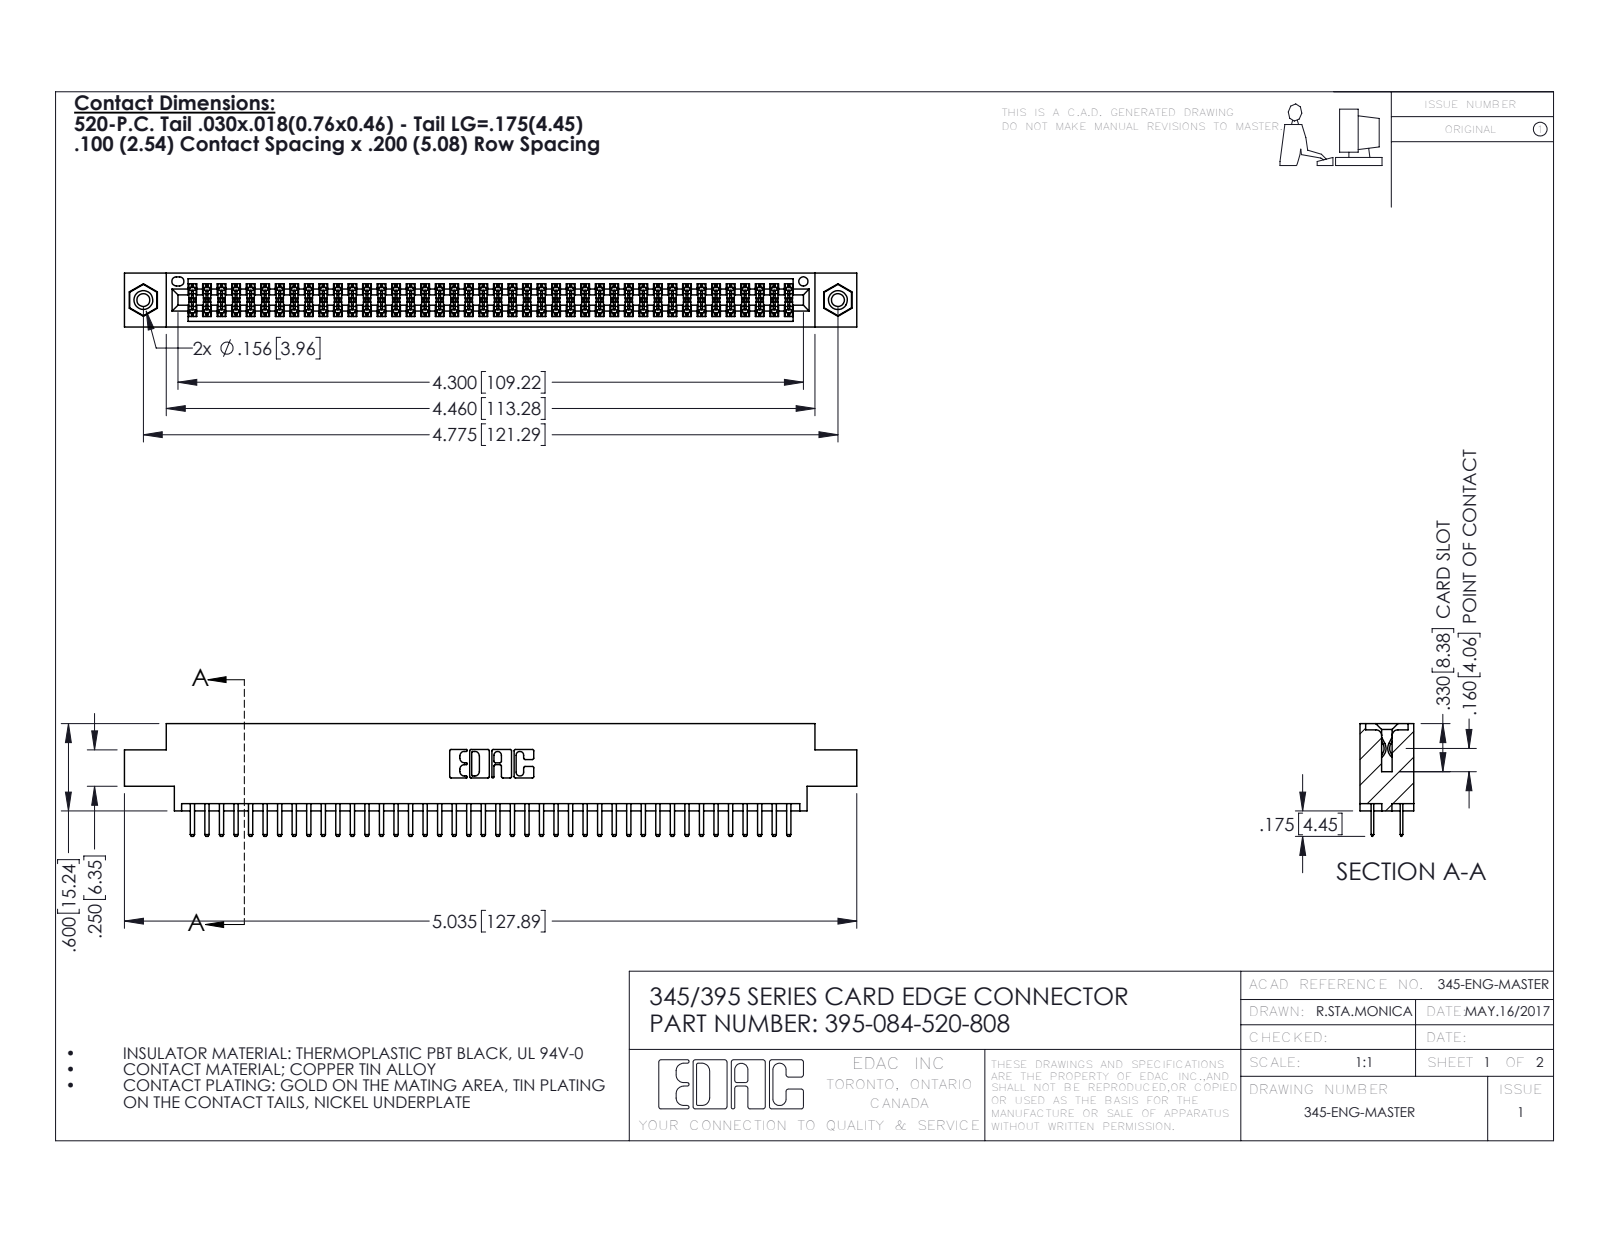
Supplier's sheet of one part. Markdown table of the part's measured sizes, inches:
| quantity | value |
| --- | --- |
| part name | 345-292-001_345-293-120; 345-250-001_345-250-003-102; 345 Part_0.170 Offset - 0.156 Dia-TI; 395-084-520-808 |
| STEP written by | SolidWorks 2016 (CONFIG_CONTROL_DESIGN) |
| units | inches |
| bodies | 87 solids, 4726 faces (3056 planar, 1654 cylindrical, 16 other) |
| overall size | 5.035 × 0.775 × 0.37 |
| volume | 0.749 in³ |
| surface area | 28.23 in² |
| round holes (diameter × count) | 0.089 × 2, 0.125 × 2, 0.156 × 2, 0.064 × 1 |
| round bosses / shafts (diameter × count) | 0.155 × 2 |
| partial cylindrical surfaces (radius × count) | 0.006 × 126, 0.01 × 88, 0.01 × 22, 0.007 × 6, 0.031 × 6, 0.026 × 3, 0.014 × 2, 0.019 × 2 |
| main face-to-face distances | 0.072, 0.298, 0.2, 0.37, 0.098, 0.272, 0.025, 0.225, 0.022, 0.175 |
| hole center spacings | 0.27, 4.539, 4.775 |
